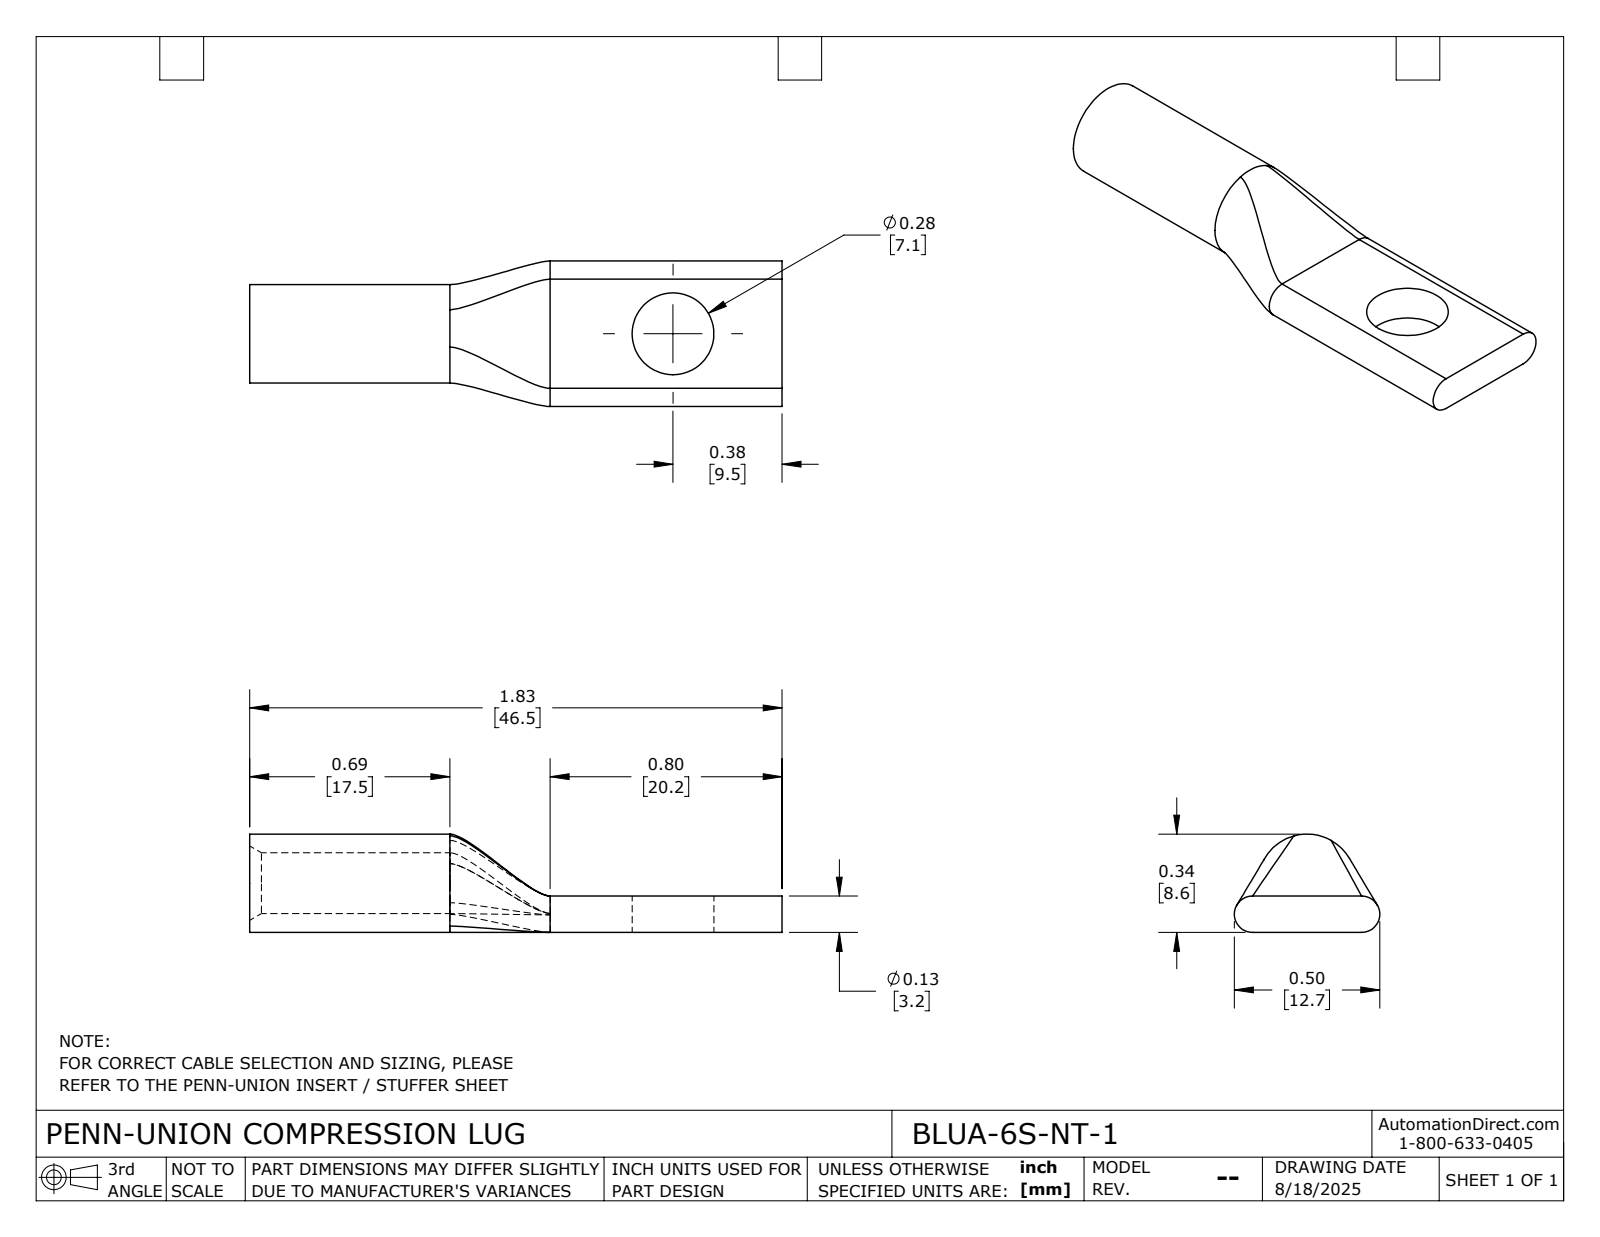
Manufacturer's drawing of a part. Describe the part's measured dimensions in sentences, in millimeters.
The part is named "BLUA-6S-NT-1". Its 3-D file was written by "SolidWorks 2024 (CONFIG_CONTROL_DESIGN)". It is 1 solid with 24 faces: 5 planar, 9 cylindrical and 10 other. Overall it measures 46.5 by 12.7 by 8.6 millimeters. Its volume is 1 600 cubic millimeters and its surface area 1 834 square millimeters. Round holes: 1 of diameter 5.3, 1 of diameter 7.1. Round bosses or shafts: 1 of diameter 8.6. Partial cylindrical surfaces (rounded edges, fillets, slot ends): 2 of radius 1.6. The main face-to-face distances are 3.2, 46.5, 26.2, 20.2.
